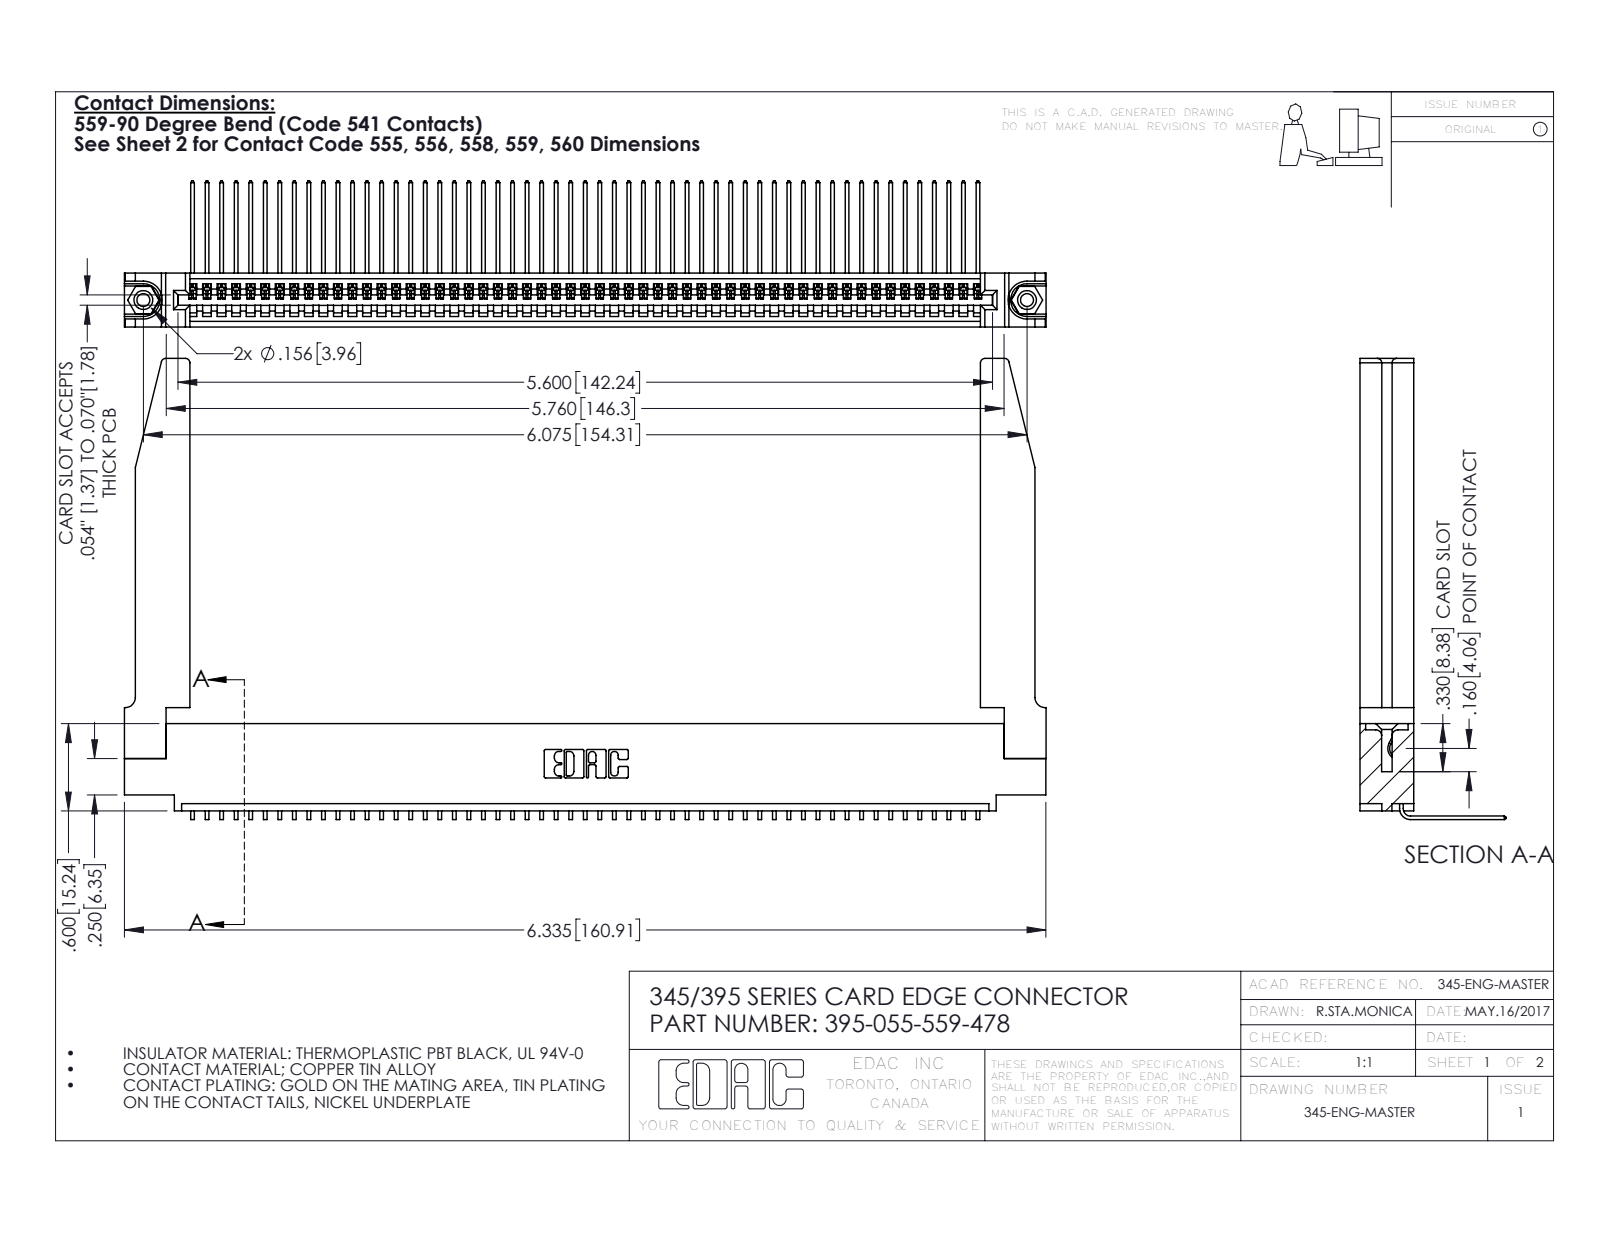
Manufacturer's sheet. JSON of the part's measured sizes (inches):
{"part_name": "345-250-001_345-250-001-102; 345-220-078_345-220-078; 345-292-001_558 559 Tail - 1; 395-055-559-478 (+1 more)", "step_written_by": "SolidWorks 2016 (CONFIG_CONTROL_DESIGN)", "units": "inches", "bodies": {"solids": 60, "faces": 3664, "planar": 2536, "cylindrical": 1076, "other": 52}, "overall_size": [6.336, 3.169, 1.005], "volume_in3": 1.42, "surface_area_in2": 44.61, "round_holes": [[0.089, 2], [0.125, 2], [0.156, 2], [0.064, 1]], "round_bosses_or_shafts": [[0.155, 2]], "partial_cylinders_radius": [[0.006, 110], [0.01, 22], [0.03, 8], [0.007, 6], [0.031, 6], [0.026, 3], [0.031, 2], [0.04, 2]], "face_to_face_distances": [0.37, 0.072, 0.298, 0.2, 0.098, 0.272, 0.025, 0.225, 0.148, 0.15], "hole_center_spacings": [0.27, 5.839, 6.075]}
